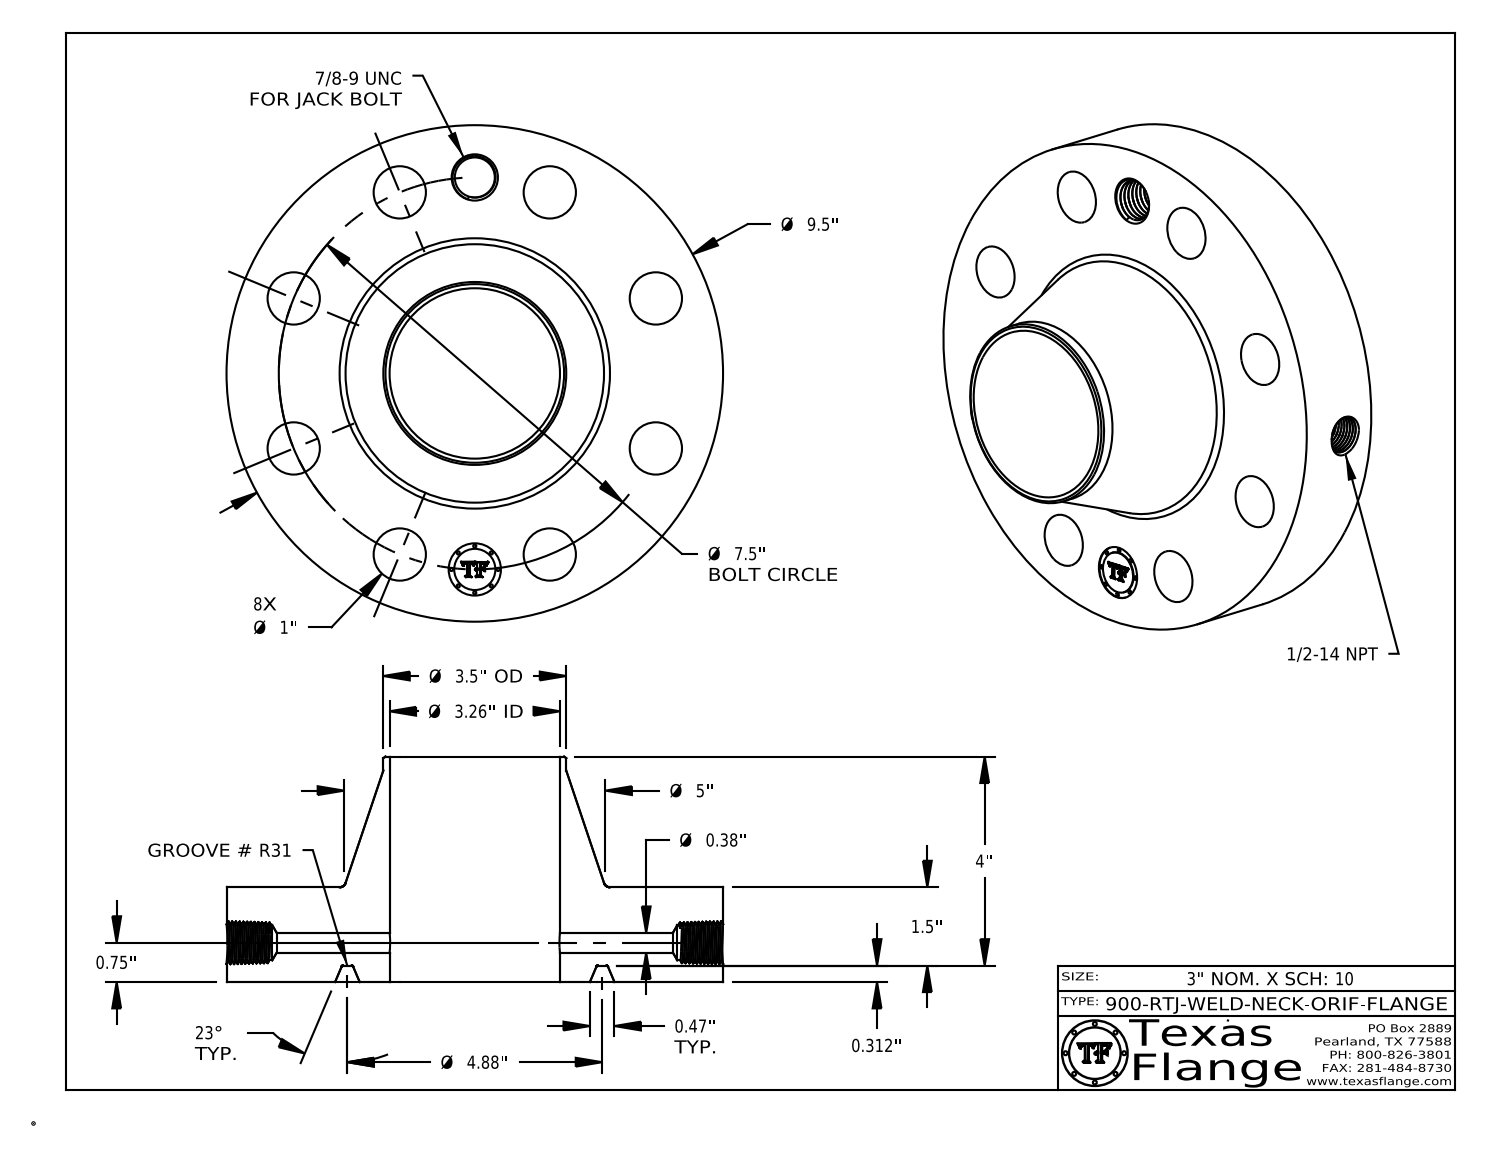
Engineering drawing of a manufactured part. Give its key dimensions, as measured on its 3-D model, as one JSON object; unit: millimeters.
{"part_name": "900-RTJ-WELD-NECK", "step_written_by": "CATIA V5 STEP AP214 (AUTOMOTIVE_DESIGN)", "units": "millimeters", "bodies": {"solids": 1, "faces": 784, "planar": 370, "cylindrical": 94, "other": 320}, "overall_size": [241.3, 241.3, 109.5], "volume_mm3": 1832000, "surface_area_mm2": 195900, "round_holes": [[25.4, 9], [9.5, 1], [17.1, 1], [19.5, 1], [82.8, 1]], "round_bosses_or_shafts": [[1.5, 8], [241.3, 1], [88.9, 1], [20, 1]], "face_to_face_distances": [46, 7.9, 38.1, 109.5, 101.6, 63.5, 45.6, 37.7, 0.4, 63.9], "hole_center_spacings": [95.3, 72.9, 134.7, 176, 190.5, 37.2, 105.8, 158.4]}
